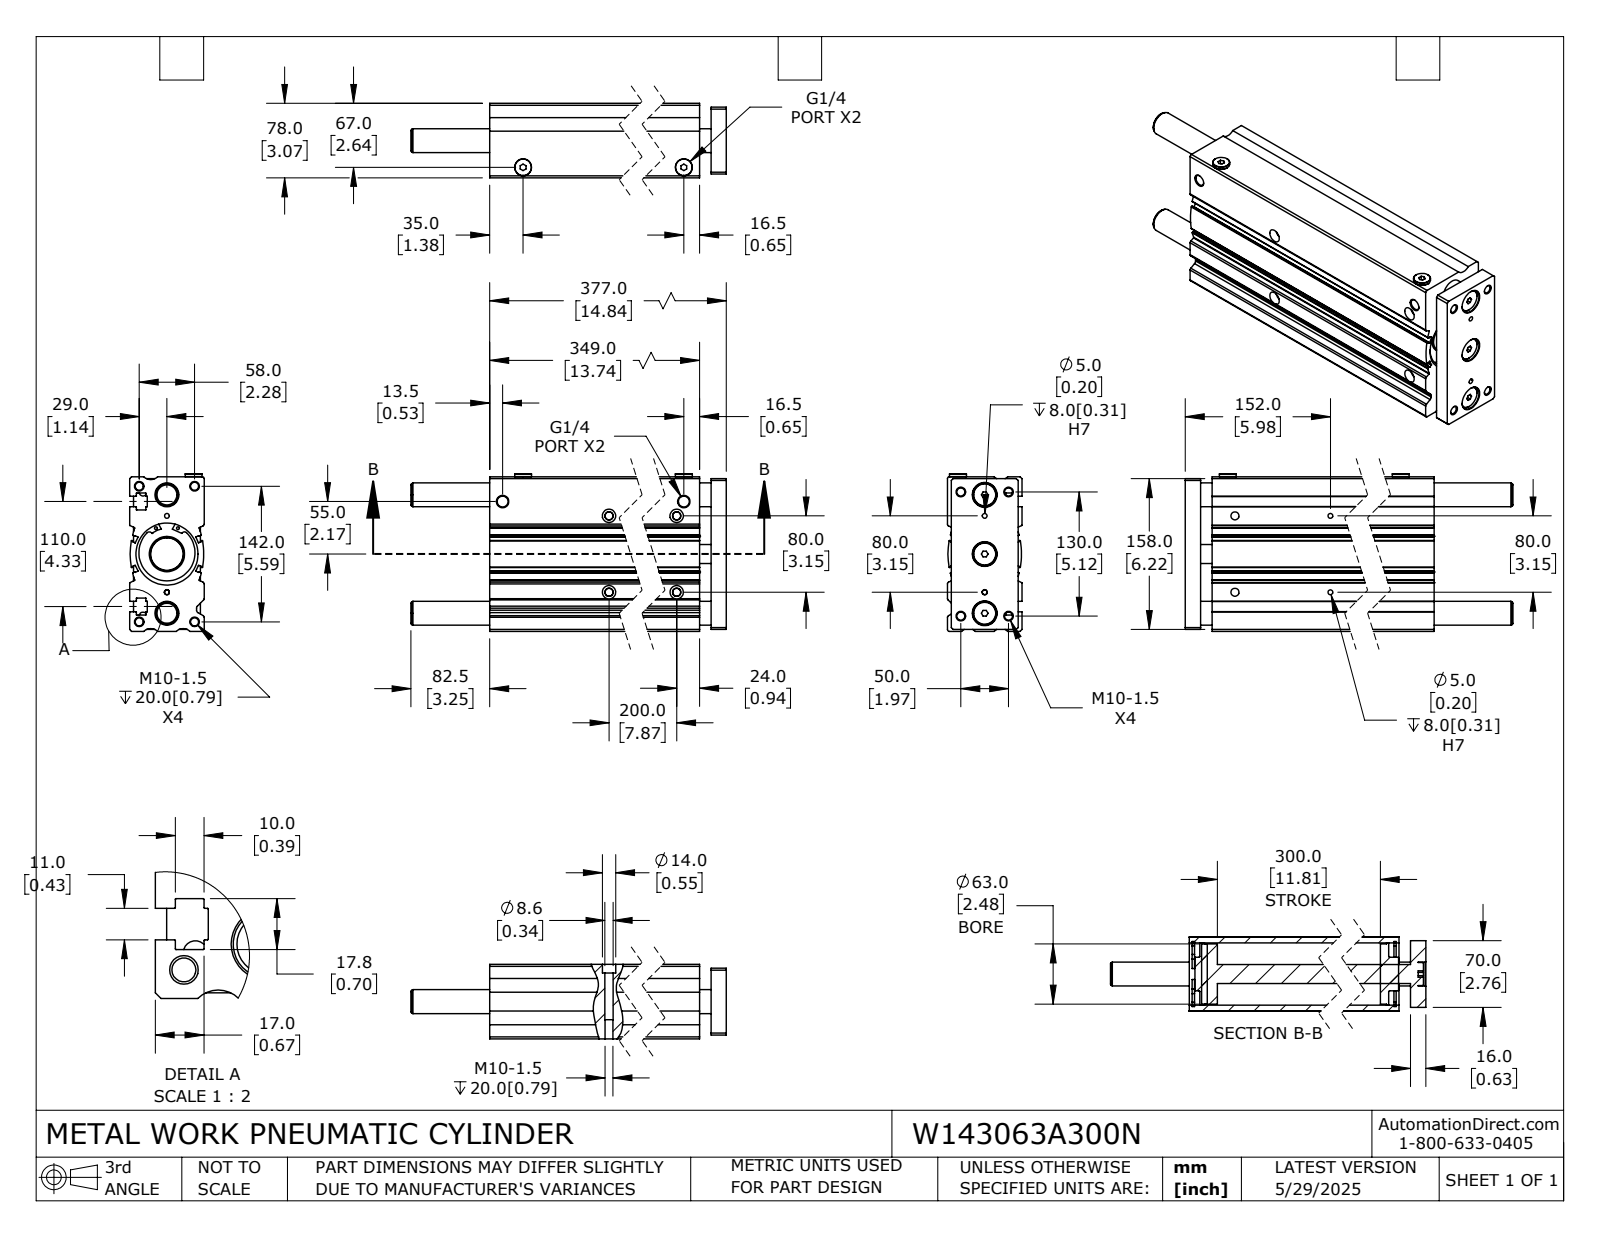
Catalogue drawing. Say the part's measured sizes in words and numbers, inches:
The part is named "W143063A300N_ROD; W143063A300N; W143063A300N_BODY". Its 3-D file was written by "SolidWorks 2024 (CONFIG_CONTROL_DESIGN)". It is 6 solids with 448 faces: 178 planar, 214 cylindrical and 56 other. Overall it measures 18.091 by 6.496 by 3.071 inches. Its volume is 202.6 cubic inches and its surface area 833.4 square inches. Round holes: 12 of diameter 0.33, 4 of diameter 0.118, 4 of diameter 0.197, 4 of diameter 0.339, 4 of diameter 0.551, 3 of diameter 0.984, 2 of diameter 0.448, 1 of diameter 2.559. Round bosses or shafts: 3 of diameter 0.945, 2 of diameter 0.697, 1 of diameter 2.677, 1 of diameter 2.551, 1 of diameter 2.48, 1 of diameter 1.378, 1 of diameter 0.787. Partial cylindrical surfaces (rounded edges, fillets, slot ends): 44 of radius 0.012, 12 of radius 0.02, 8 of radius 0.079, 4 of radius 0.118, 3 of radius 0.394, 2 of radius 0.098, 2 of radius 0.124, 2 of radius 1.157. The main face-to-face distances are 3.071, 6.378, 4.331, 0.134, 0.567, 0.728, 0.63, 2.343, 0.472, 1.102. The hole center spacings are 0.284, 0.682, 0.991, 1.158, 1.195, 1.392, 1.448, 1.585.
